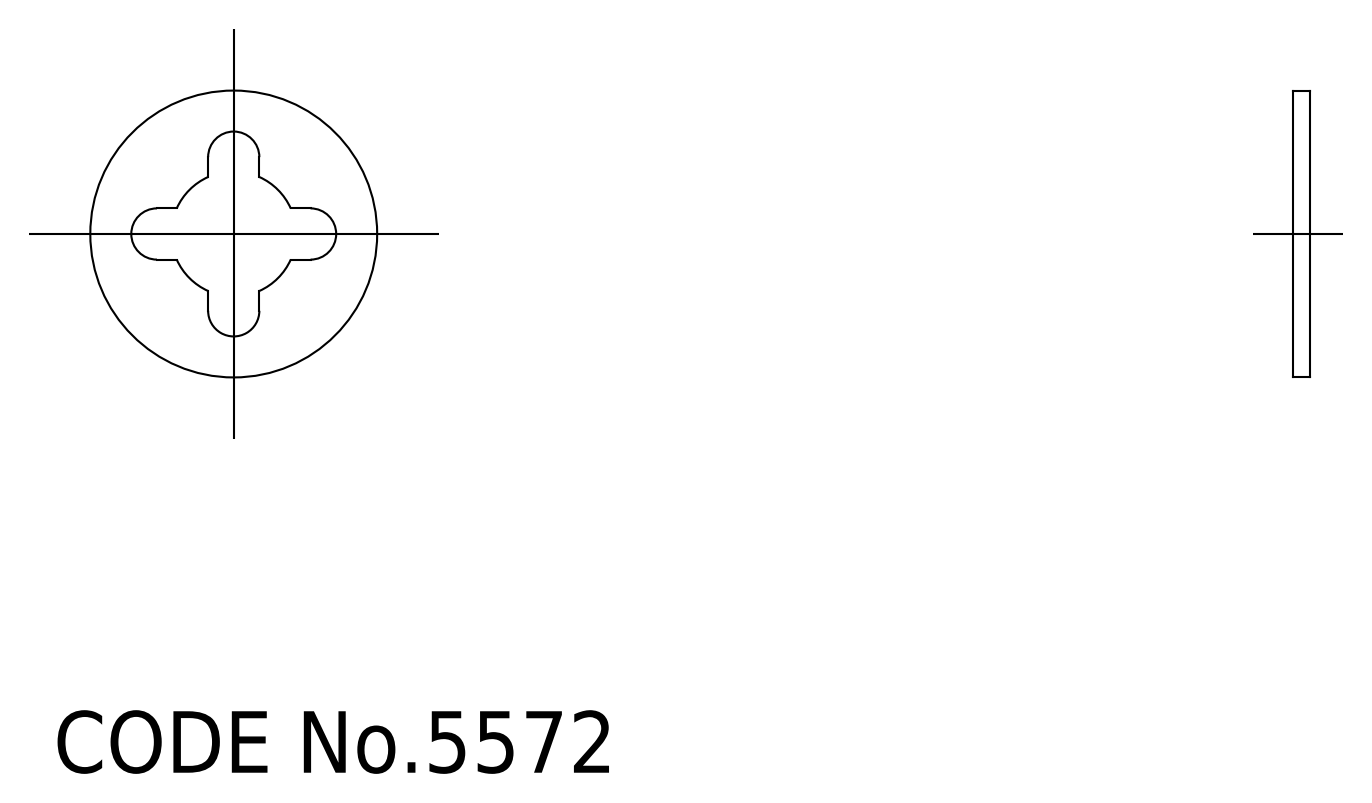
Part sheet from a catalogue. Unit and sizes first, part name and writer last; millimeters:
Units: millimetres
Overall size (bounding box): 14 × 14 × 0.8
Volume: 86 mm³ · Surface area: 275 mm²
Bodies: 1 solid, 20 faces (0 planar, 0 cylindrical, 20 other)
Part name (STEP PRODUCT): washer
STEP written by: CADfix (AUTOMOTIVE_DESIGN)
